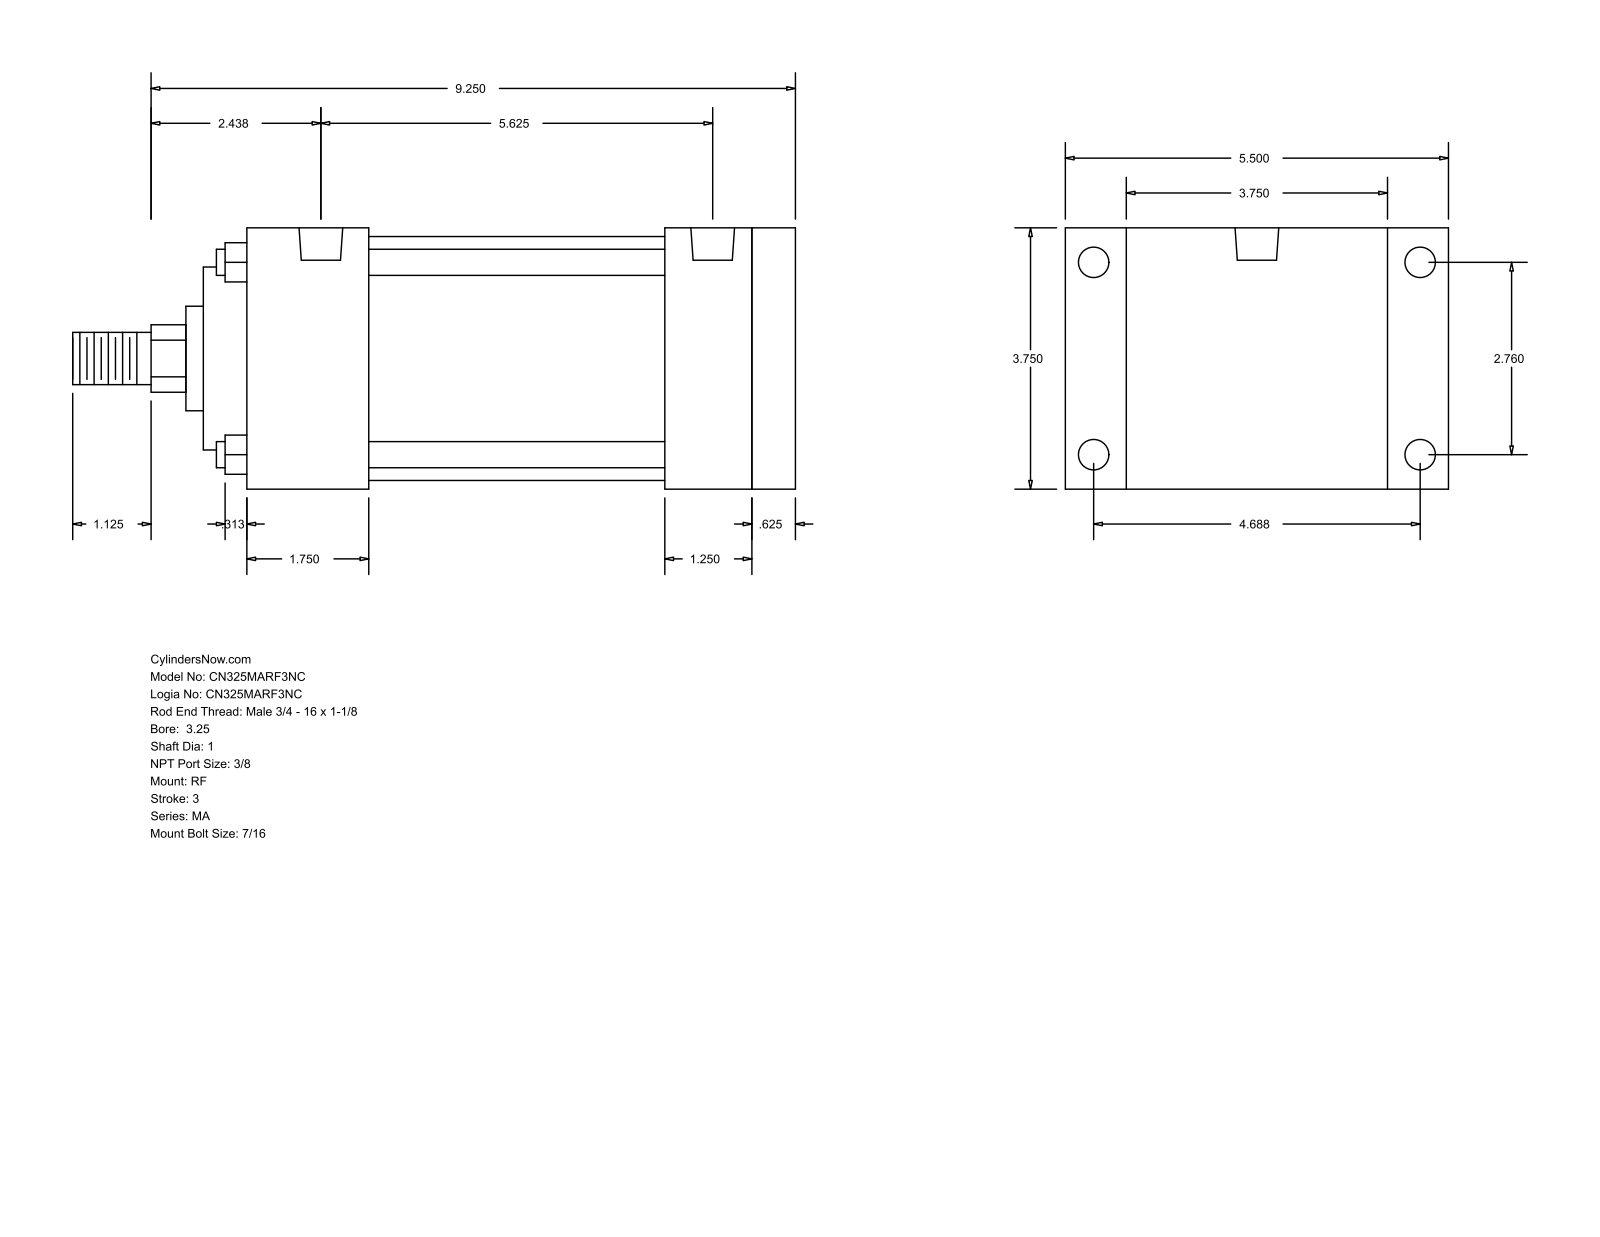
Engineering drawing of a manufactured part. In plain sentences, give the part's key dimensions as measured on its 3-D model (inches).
The part is named "MA_RF__0325_1". Its 3-D file was written by "GSSL Pune (CONFIG_CONTROL_DESIGN)". It is 0 solids with 94 faces: 65 planar, 29 cylindrical and 0 other. Overall it measures 10.375 by 5.5 by 3.75 inches. Round holes: 8 of diameter 0.437, 2 of diameter 0.627. Round bosses or shafts: 4 of diameter 0.375, 1 of diameter 3.5, 1 of diameter 2.625, 1 of diameter 1.5, 1 of diameter 1, 1 of diameter 0.75. Partial cylindrical surfaces (rounded edges, fillets, slot ends): 1 of radius 0.484. The main face-to-face distances are 3.75, 7.875, 7.25, 0.625, 0.875, 4.625, 6, 1.25, 1.875, 1.75. The hole center spacings are 0.187, 2.76, 4.687, 5.25, 5.438, 5.439, 5.625.
